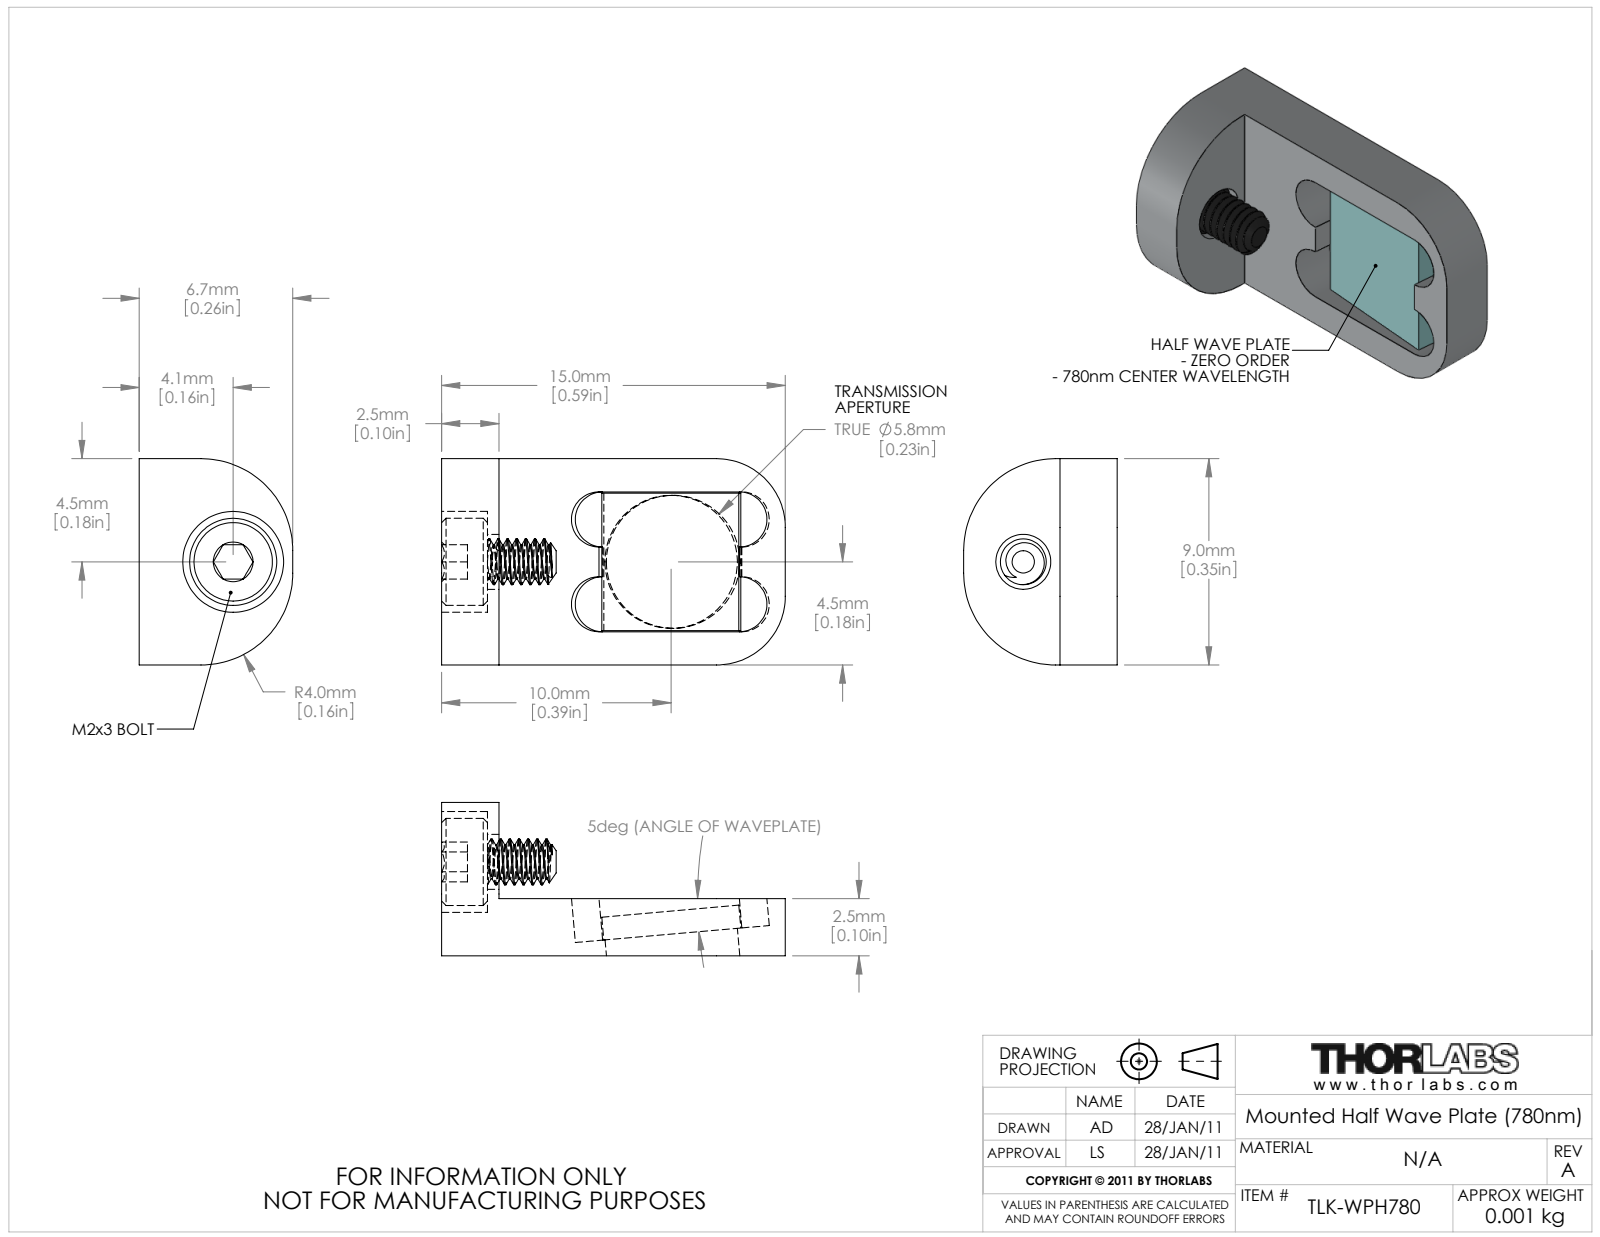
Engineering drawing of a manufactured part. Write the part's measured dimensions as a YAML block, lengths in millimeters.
part_name: "21899-E0W"
step_written_by: "SolidWorks 2009 (AUTOMOTIVE_DESIGN)"
units: millimeters
bodies: {solids: 3, faces: 92, planar: 30, cylindrical: 47, other: 15}
overall_size: [15, 9, 6.7]
volume: 339
surface_area: 655
round_holes:
  - {diameter: 2.4, count: 1}
  - {diameter: 4.4, count: 1}
  - {diameter: 5.8, count: 1}
round_bosses_or_shafts:
  - {diameter: 3.8, count: 1}
  - {diameter: 2, count: 1}
  - {diameter: 1.48, count: 1}
partial_cylinders:
  - {radius: 1.2, count: 4}
  - {radius: 3, count: 2}
  - {radius: 4, count: 2}
face_to_face_distances: [2.5, 1, 9, 1.45, 7.55, 2, 0.5, 6.05, 1.5, 7.5]
